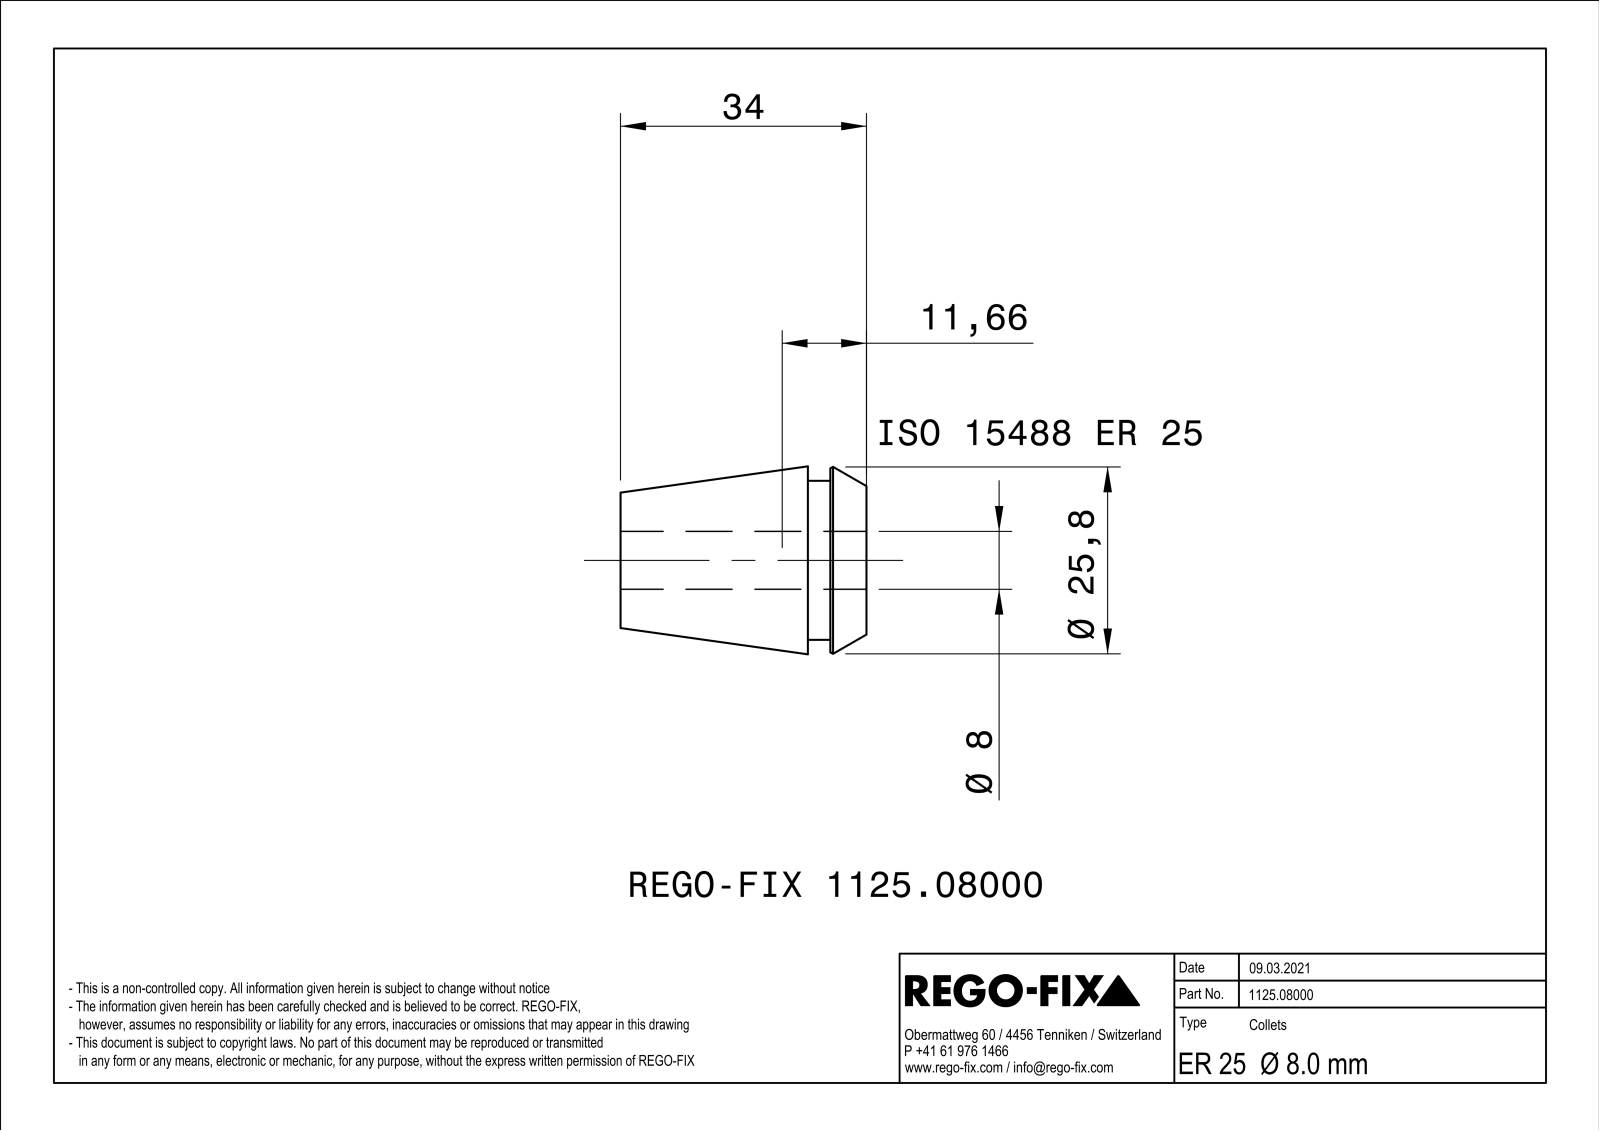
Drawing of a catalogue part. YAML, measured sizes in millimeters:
part_name: "NOCUT"
step_written_by: "SIEMENS PLM Software Solid Edge ST10 (AUTOMOTIVE_DESIGN)"
units: millimeters
bodies: {solids: 1, faces: 177, planar: 72, cylindrical: 25, other: 80}
overall_size: [34, 25.99, 25.99]
volume: 9117
surface_area: 10211
round_holes:
  - {diameter: 8, count: 1}
round_bosses_or_shafts:
  - {diameter: 22, count: 1}
partial_cylinders:
  - {radius: 0.4, count: 8}
face_to_face_distances: [0.8, 34, 8.1, 25.9, 5, 3.1, 29]
